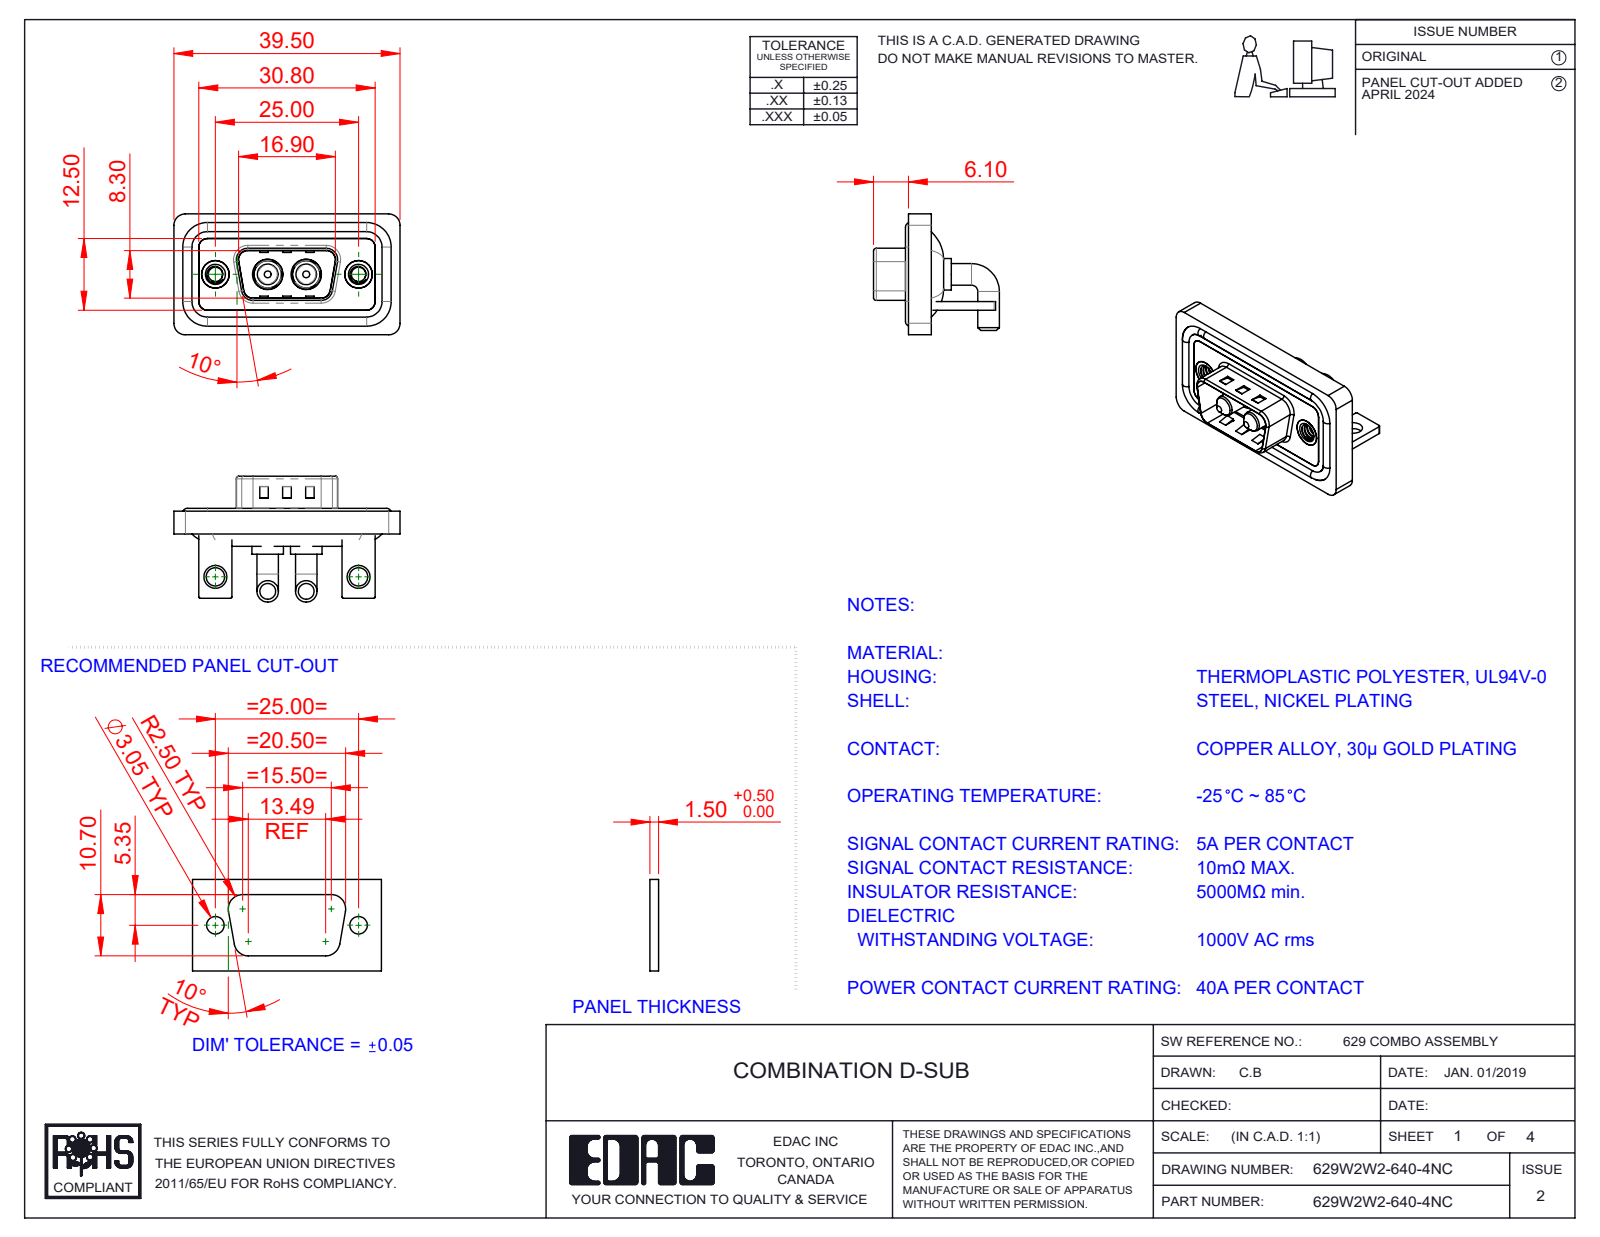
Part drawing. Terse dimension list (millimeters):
name: 629Combo Shell Front_09 Contacts; 629Combo Shell Rear_09 Contacts; 629Combo Threaded Rivet_B; Power Pin_40A RA (+4 more)
written by: SolidWorks 2023 (CONFIG_CONTROL_DESIGN)
unit: mm
bodies: 13 solids, 535 faces (185 planar, 240 cylindrical, 110 other)
size: 39.5 × 21.98 × 21.1
volume: 5 002 mm³; area: 7 843 mm²
holes: 2× ⌀2.5, 2× ⌀3.2, 2× ⌀4, 2× ⌀4.8, 2× ⌀4.85, 2× ⌀5, 2× ⌀5.3
bosses: 4× ⌀3.75, 4× ⌀1.6, 2× ⌀5.5, 2× ⌀5.2, 2× ⌀4.9, 2× ⌀4.75, 2× ⌀3.6
rounds: 19× R2, 18× R1.5, 16× R0.25, 9× R0.5, 8× R1.6, 4× R0.6, 4× R0.65, 4× R0.9
face distances: 0.4, 1.5, 2.9, 0.8, 1.1, 1.2, 2.1, 1.6, 3.7, 2.5
hole spacings: 9.14, 15.86, 25, 6.72
